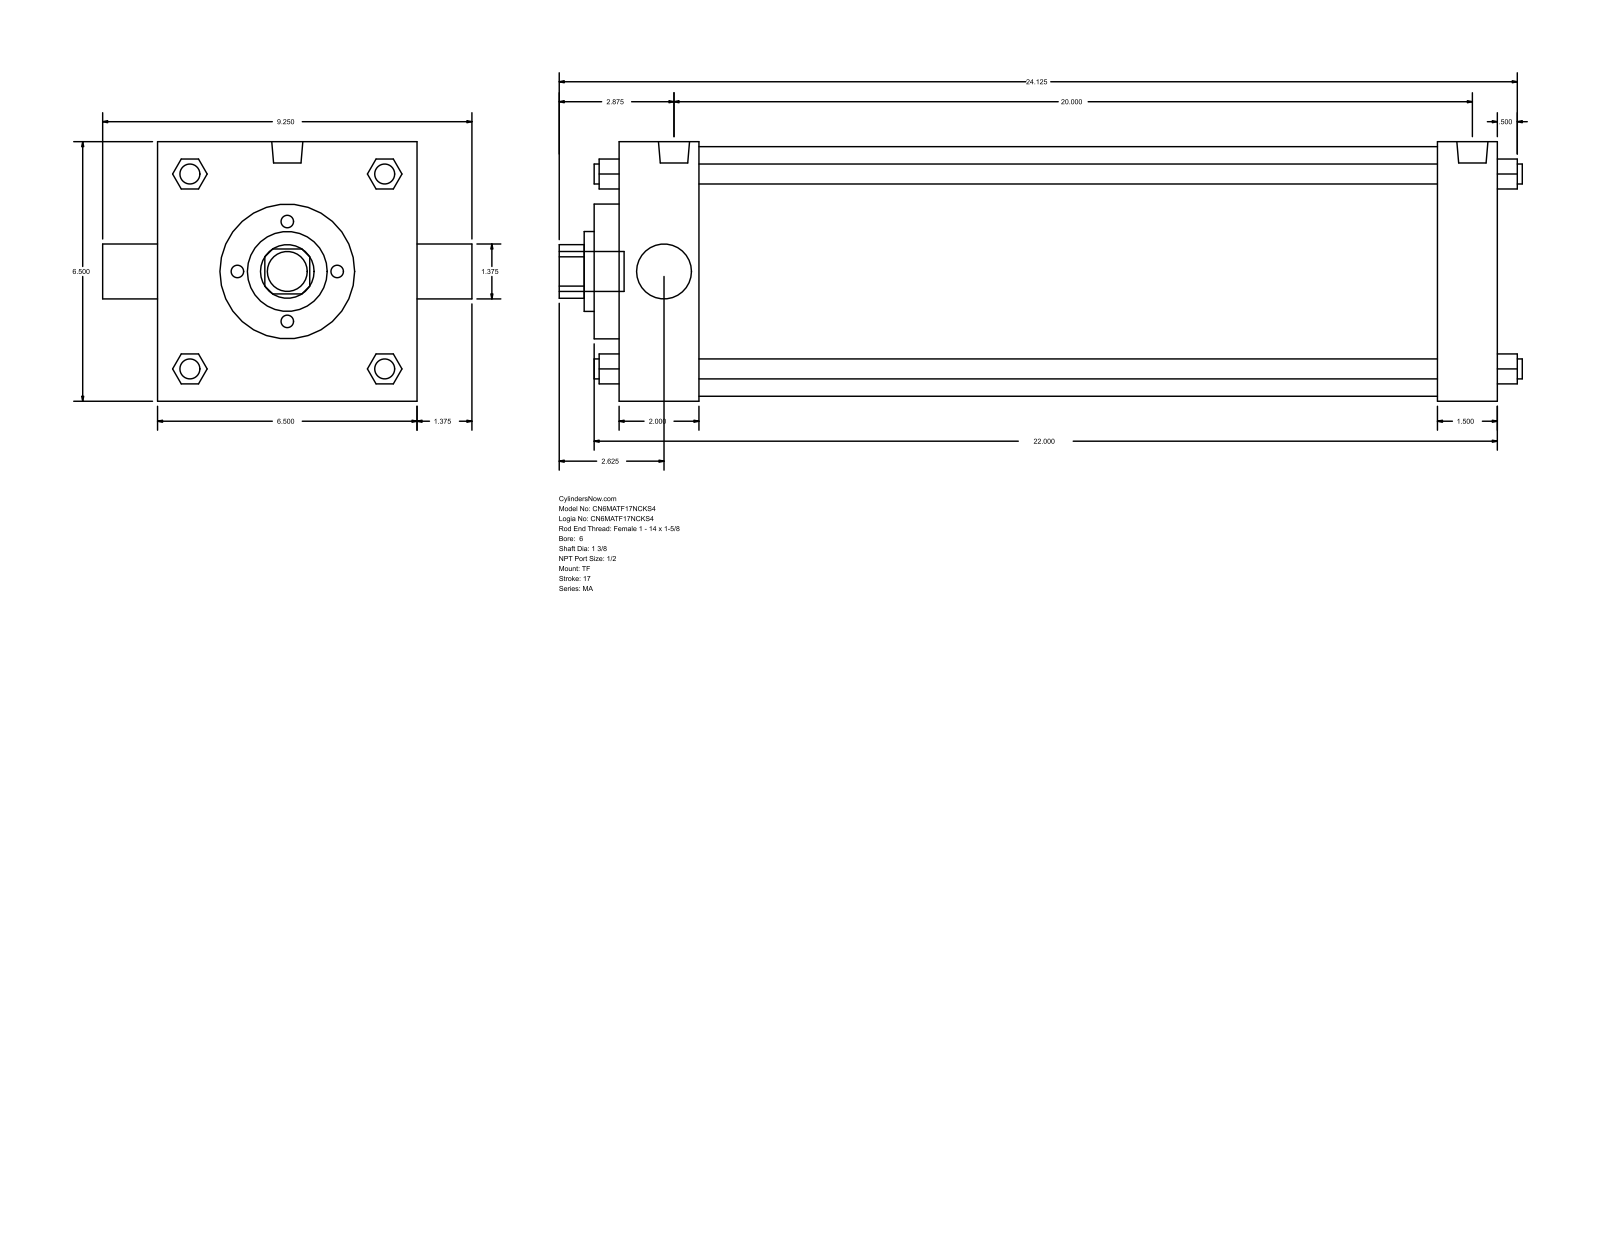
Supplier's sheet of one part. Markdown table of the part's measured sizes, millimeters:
| quantity | value |
| --- | --- |
| part name | MA_TF__0600_1.375 |
| STEP written by | GSSL Pune (CONFIG_CONTROL_DESIGN) |
| units | millimeters |
| bodies | 0 solids, 122 faces (93 planar, 29 cylindrical, 0 other) |
| overall size | 612.77 × 234.95 × 165.1 |
| round holes (diameter × count) | 34.92 × 2, 50.8 × 1, 85.72 × 1, 158.75 × 1 |
| round bosses / shafts (diameter × count) | 12.7 × 4, 17.46 × 3, 19.77 × 2, 25.4 × 1 |
| partial cylindrical surfaces (radius × count) | 17.06 × 1 |
| main face-to-face distances | 165.1, 561.98, 38.1, 50.8, 511.18, 523.88, 473.08, 15.87, 66.67, 539.75 |
